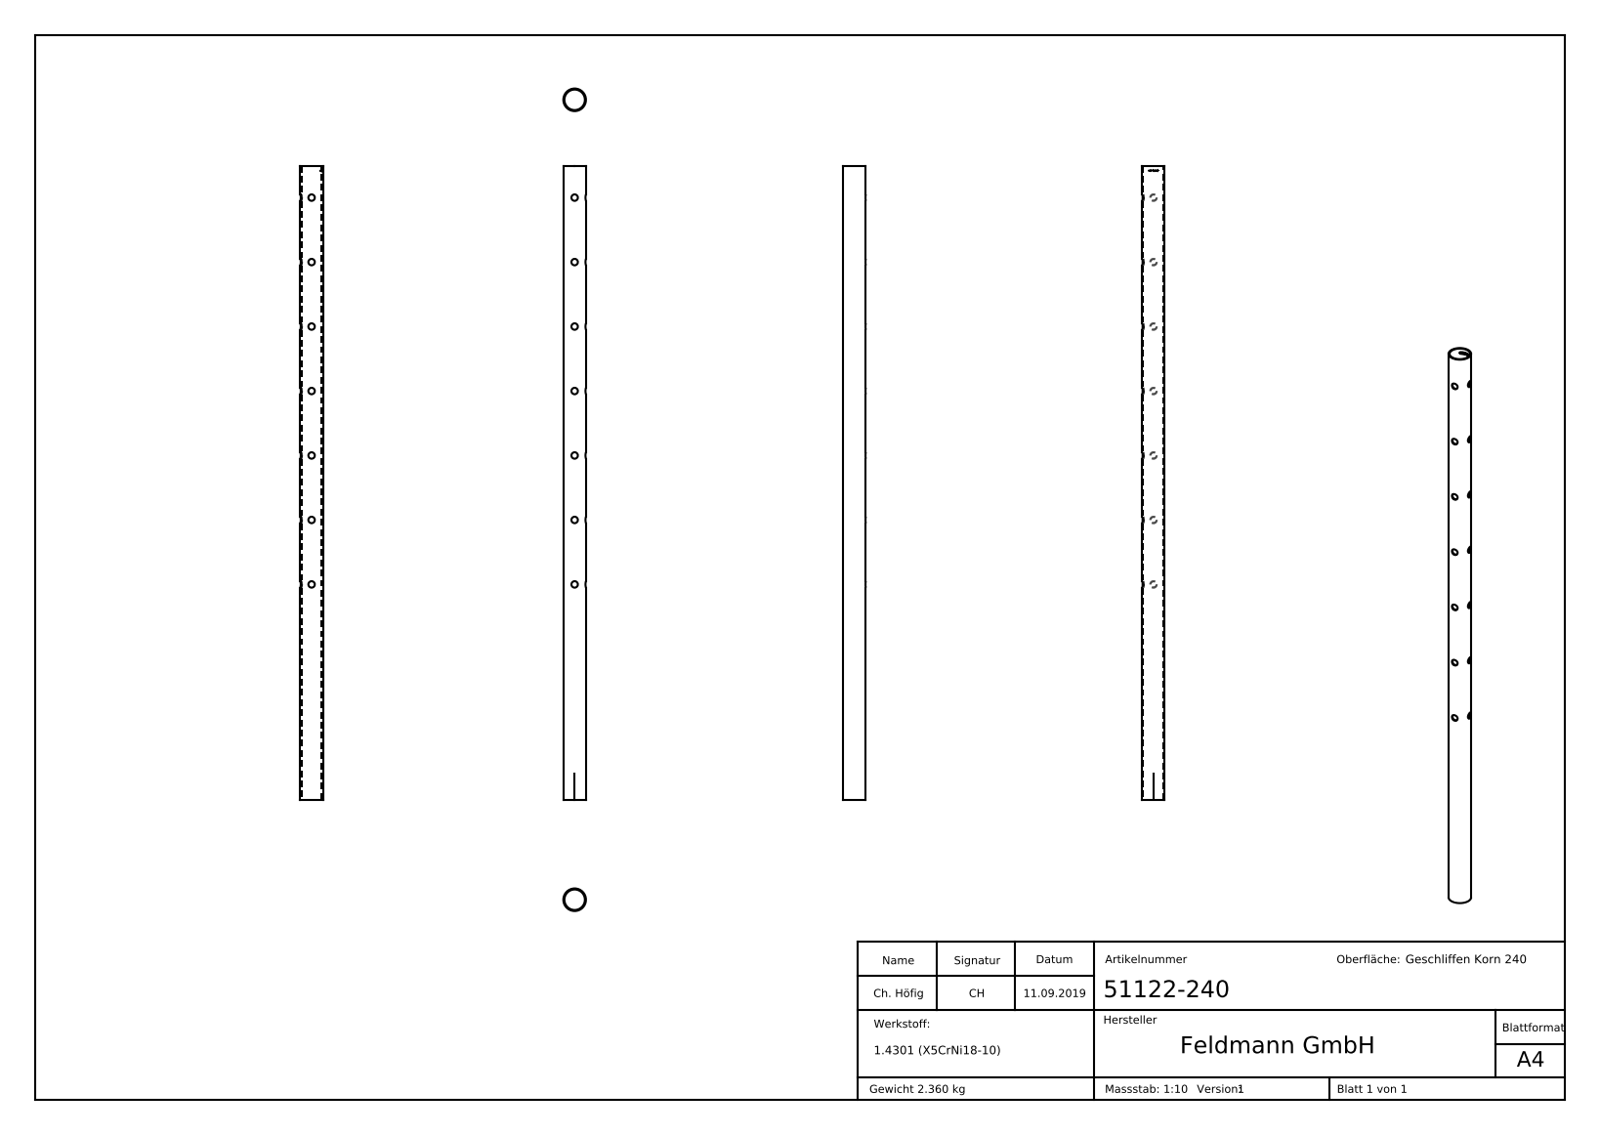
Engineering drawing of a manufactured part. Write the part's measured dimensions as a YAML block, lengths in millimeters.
part_name: "51122-240"
step_written_by: "SolidWorks 2015 (CONFIG_CONTROL_DESIGN)"
units: millimeters
bodies: {solids: 1, faces: 246, planar: 109, cylindrical: 54, other: 83}
overall_size: [1190, 42.4, 42.4]
volume: 298811
surface_area: 300420
round_holes:
  - {diameter: 12.1, count: 14}
  - {diameter: 38.4, count: 1}
round_bosses_or_shafts:
  - {diameter: 42.4, count: 1}
partial_cylinders:
  - {radius: 19.3, count: 1}
face_to_face_distances: [1190, 10, 1180, 2.97, 1.01, 0.44, 1.32, 1.19, 0.39, 0.74]
hole_center_spacings: [121, 242, 363, 484, 605, 726]
